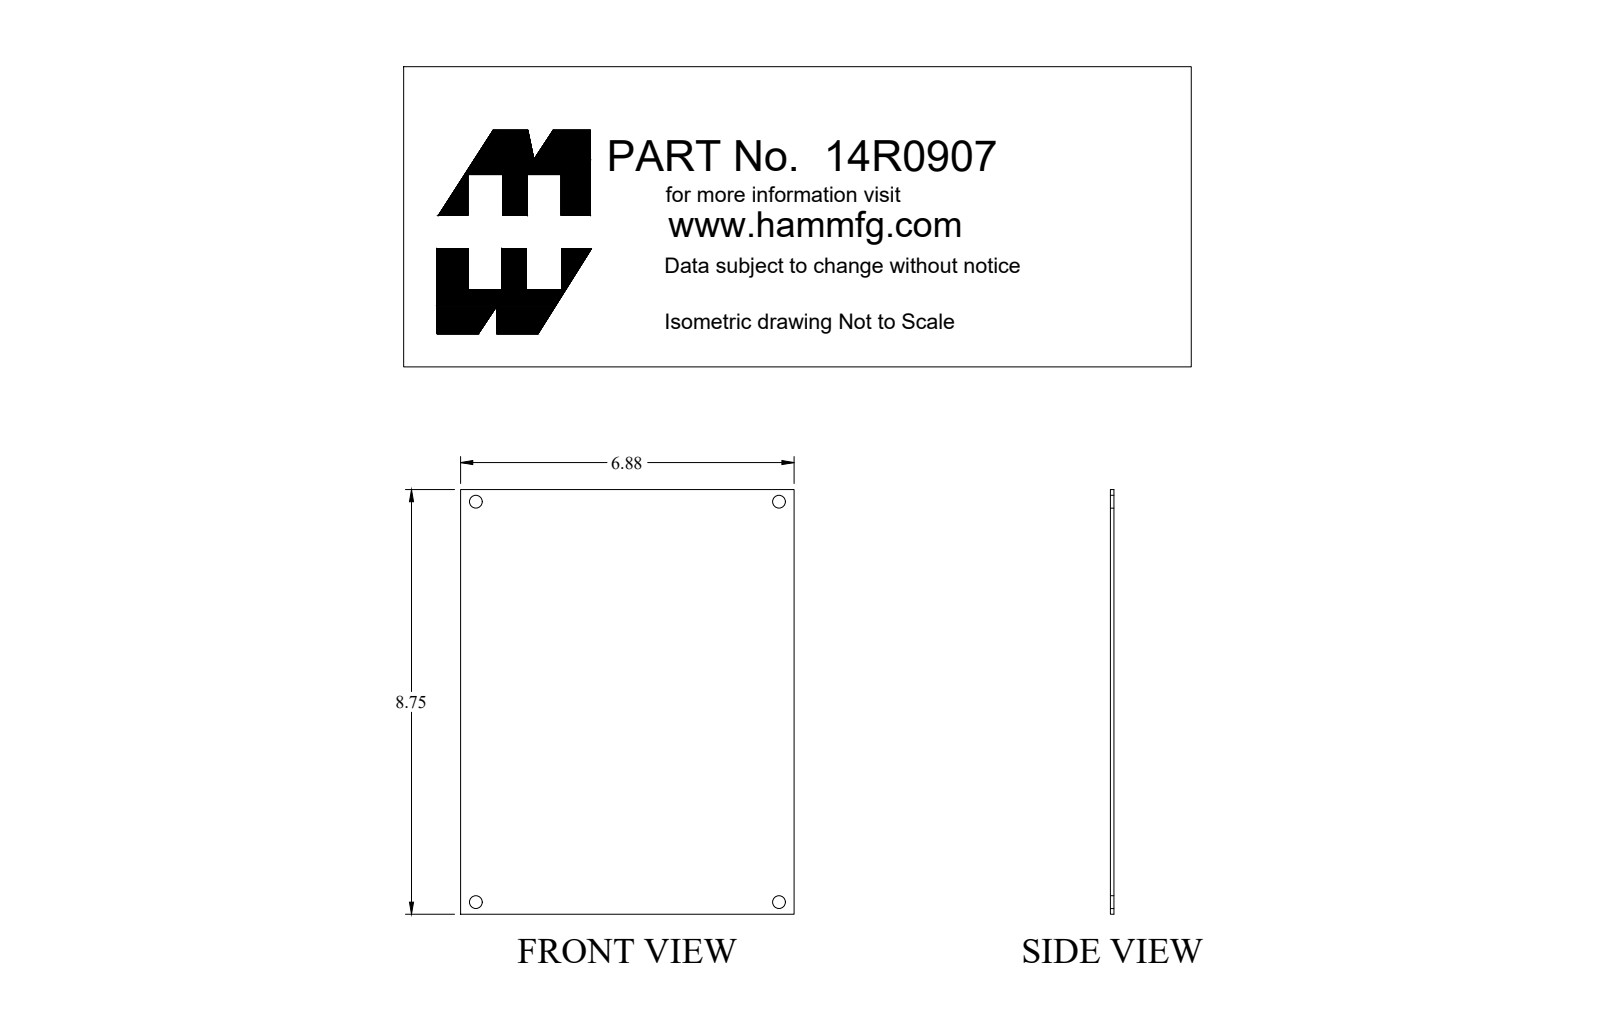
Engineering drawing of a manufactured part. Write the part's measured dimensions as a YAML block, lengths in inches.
part_name: "14R0907"
step_written_by: "SolidWorks 2018 (AUTOMOTIVE_DESIGN)"
units: inches
bodies: {solids: 1, faces: 10, planar: 6, cylindrical: 4, other: 0}
overall_size: [8.75, 6.875, 0.072]
volume: 4.315
surface_area: 122.4
round_holes:
  - {diameter: 0.265, count: 4}
face_to_face_distances: [0.072, 6.875, 8.75]
hole_center_spacings: [6.25, 8.25, 10.35]
